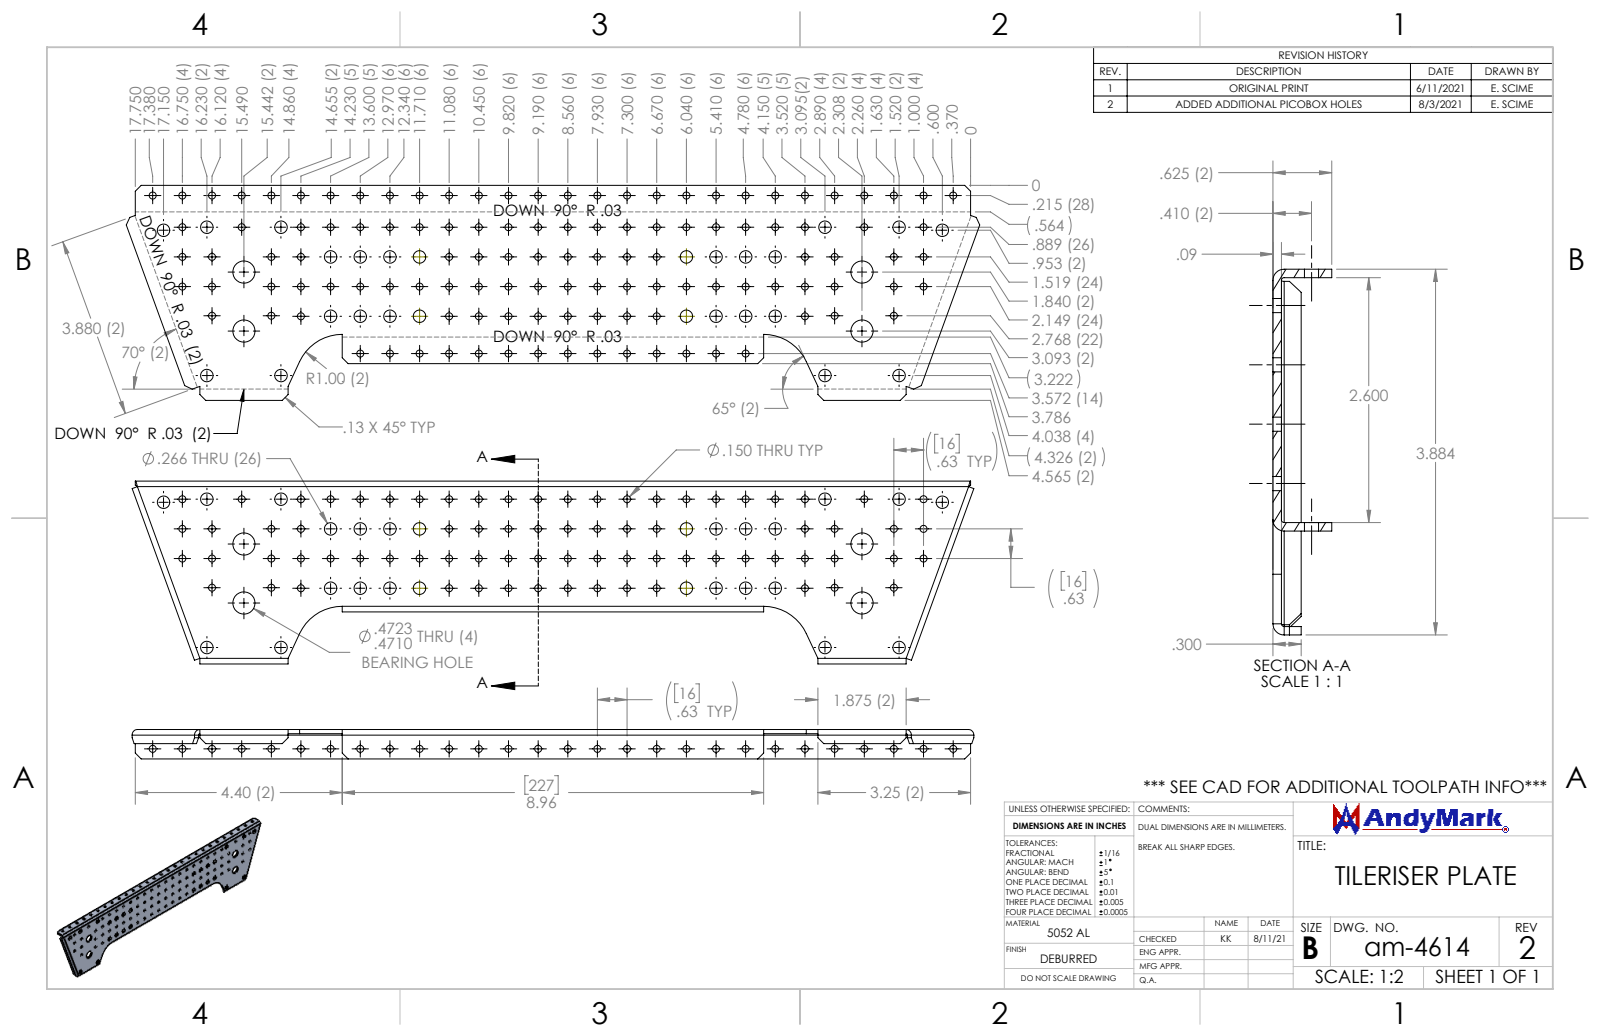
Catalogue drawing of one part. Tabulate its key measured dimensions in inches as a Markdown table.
| quantity | value |
| --- | --- |
| part name | am-4614 TileRiser Plate |
| STEP written by | SolidWorks 2021 (CONFIG_CONTROL_DESIGN) |
| units | inches |
| bodies | 1 solid, 372 faces (62 planar, 310 cylindrical, 0 other) |
| overall size | 17.8 × 3.884 × 0.625 |
| volume | 5.715 in³ |
| surface area | 138.6 in² |
| round holes (diameter × count) | 0.15 × 104, 0.266 × 26, 0.472 × 4 |
| partial cylindrical surfaces (radius × count) | 0.029 × 5, 0.119 × 5, 1 × 2 |
| main face-to-face distances | 0.09, 0.09, 2.6, 2.69, 2.69, 2.78, 0.535, 0.625, 1.104, 1.014 |
| hole center spacings | 0.63, 1.26, 3.15, 6.3, 1.89, 2.52, 6.93, 3.78 |
